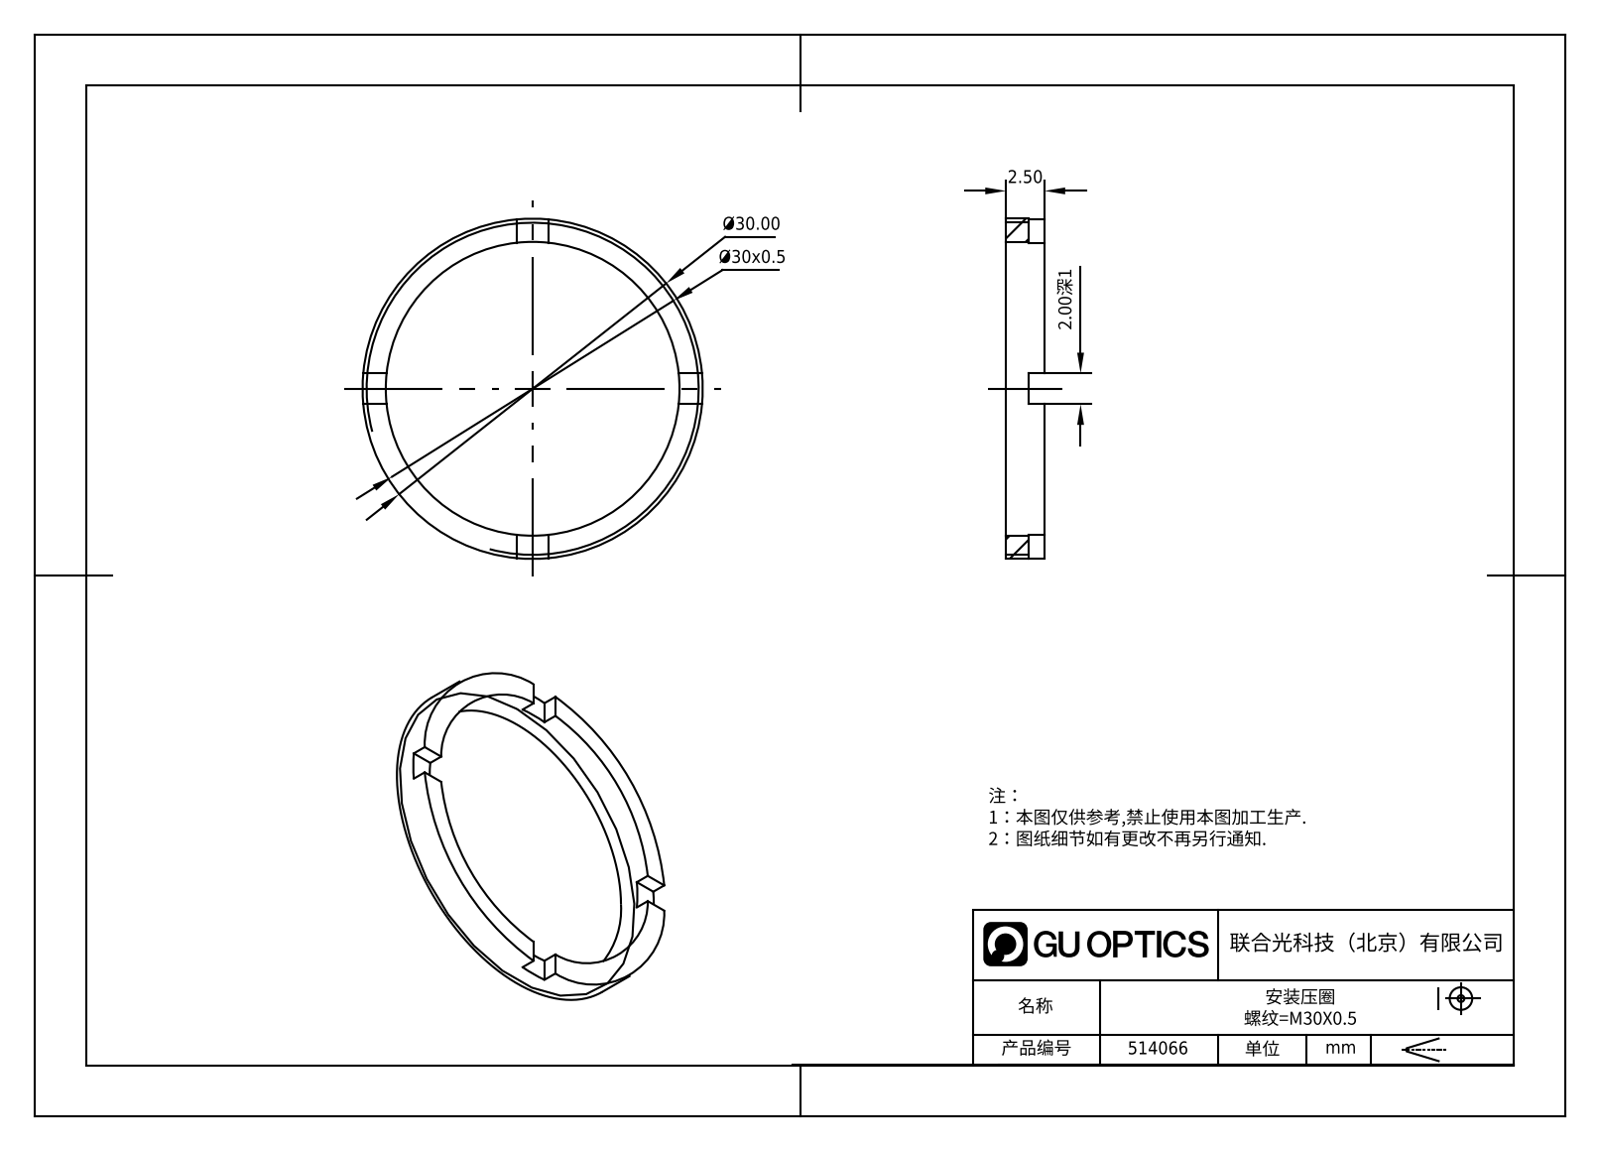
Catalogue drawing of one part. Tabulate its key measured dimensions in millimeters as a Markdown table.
| quantity | value |
| --- | --- |
| part name | 514066 |
| STEP written by | SolidWorks 2020 (CONFIG_CONTROL_DESIGN) |
| units | millimeters |
| bodies | 1 solid, 21 faces (17 planar, 4 cylindrical, 0 other) |
| overall size | 30 × 30 × 2.5 |
| volume | 424 mm³ |
| surface area | 792 mm² |
| round holes (diameter × count) | 26 × 1 |
| round bosses / shafts (diameter × count) | 30 × 1 |
| main face-to-face distances | 2.5, 1.5, 1, 2 |
